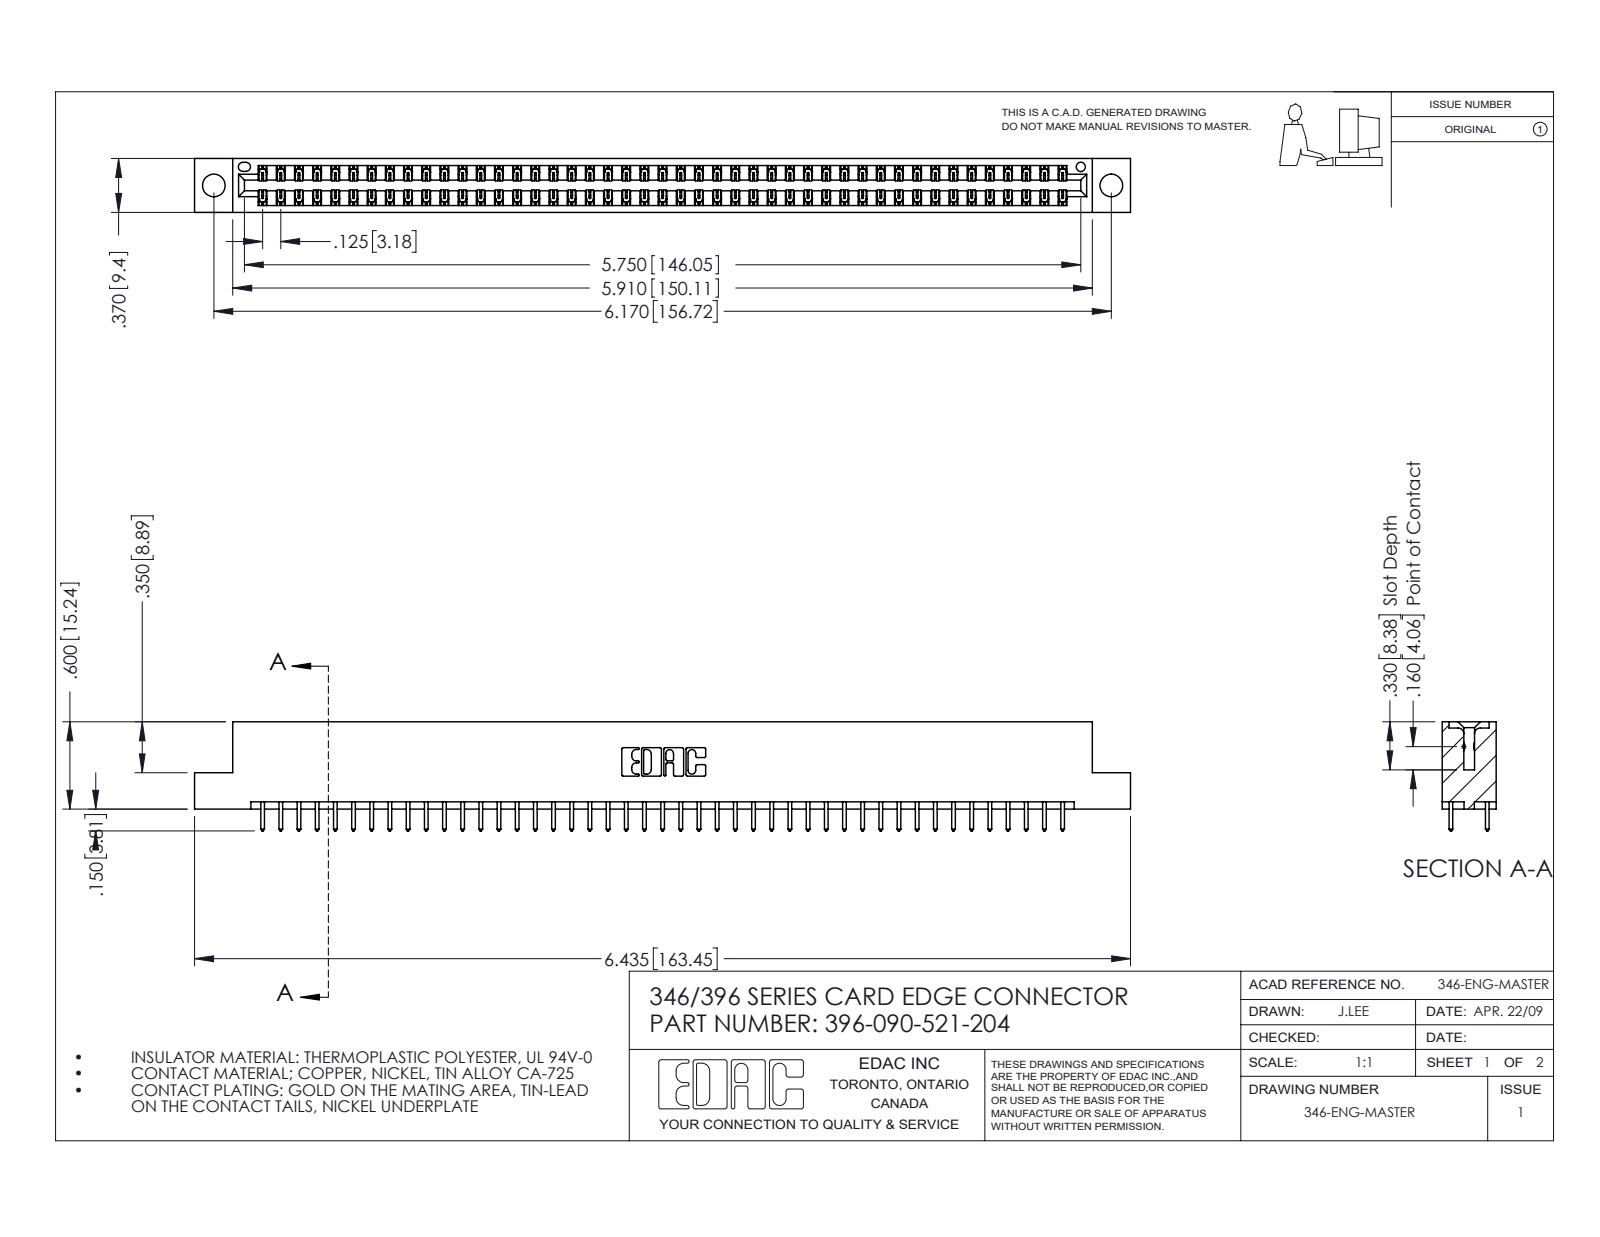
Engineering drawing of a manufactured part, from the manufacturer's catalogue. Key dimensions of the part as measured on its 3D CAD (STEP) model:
Part name (STEP PRODUCT): 346 Part_Flush Mounting Lugs - 0.156 Dia-TH; 345-292-001_345-293-121; 396-090-521-204
STEP written by: SolidWorks 2016 (CONFIG_CONTROL_DESIGN)
Units: inches
Bodies: 91 solids, 4802 faces (3226 planar, 1576 cylindrical, 0 other)
Overall size (bounding box): 6.435 × 0.75 × 0.37
Volume: 0.966 in³ · Surface area: 33.14 in²
Round holes (diameter × count): ⌀0.156 ×2, ⌀0.064 ×1
Partial cylindrical surfaces — rounded edges, fillets, slot ends (radius × count): R0.006 ×135, R0.01 ×90, R0.01 ×22, R0.007 ×6, R0.031 ×6, R0.026 ×3, R0.014 ×2, R0.022 ×2
Main face-to-face distances: 0.048, 0.322, 0.25, 0.37, 0.072, 0.298, 0.025, 0.275, 0.148, 0.222
Hole centre spacings: 0.246, 5.961, 6.17
